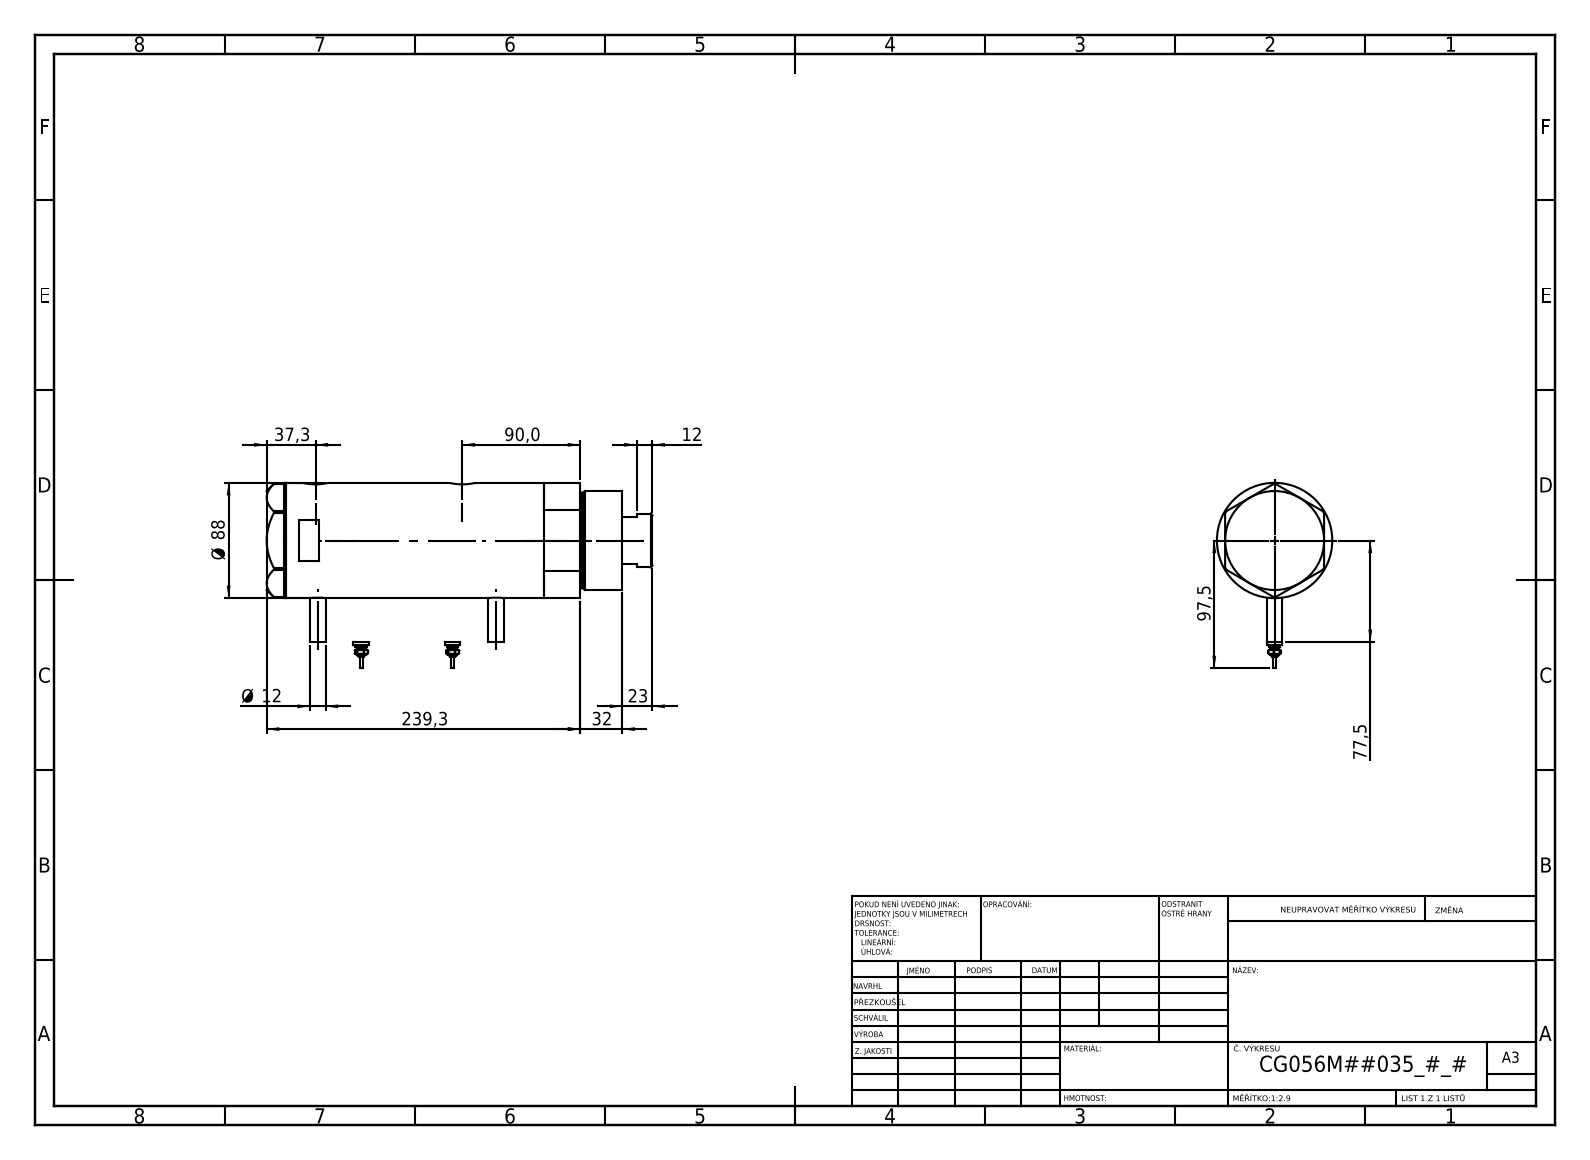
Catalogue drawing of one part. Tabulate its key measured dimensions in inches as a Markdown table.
| quantity | value |
| --- | --- |
| part name | V270CG_VC; V270CG_BACK; V270CG_MIDDLE; V270CG_FRONT (+1 more) |
| STEP written by | SolidWorks 2019 (CONFIG_CONTROL_DESIGN) |
| units | inches |
| bodies | 6 solids, 213 faces (80 planar, 69 cylindrical, 64 other) |
| overall size | 11.587 × 5.571 × 3.465 |
| volume | 95.01 in³ |
| surface area | 349.1 in² |
| round holes (diameter × count) | 0.492 × 2, 0.518 × 2, 0.787 × 2, 0.571 × 1, 1.654 × 1, 1.713 × 1, 2.205 × 1, 2.362 × 1, 3.15 × 1 |
| round bosses / shafts (diameter × count) | 0.472 × 4, 0.354 × 2, 0.276 × 2, 0.177 × 2, 0.098 × 2, 3.465 × 1, 2.953 × 1, 2.874 × 1 |
| main face-to-face distances | 5.291, 1.024, 4.268, 0.591, 1.614, 5.882, 10.091, 10.681, 9.067, 4.799 |
| hole center spacings | 0.067, 1.016, 4.343, 4.409, 5.358, 5.425 |
